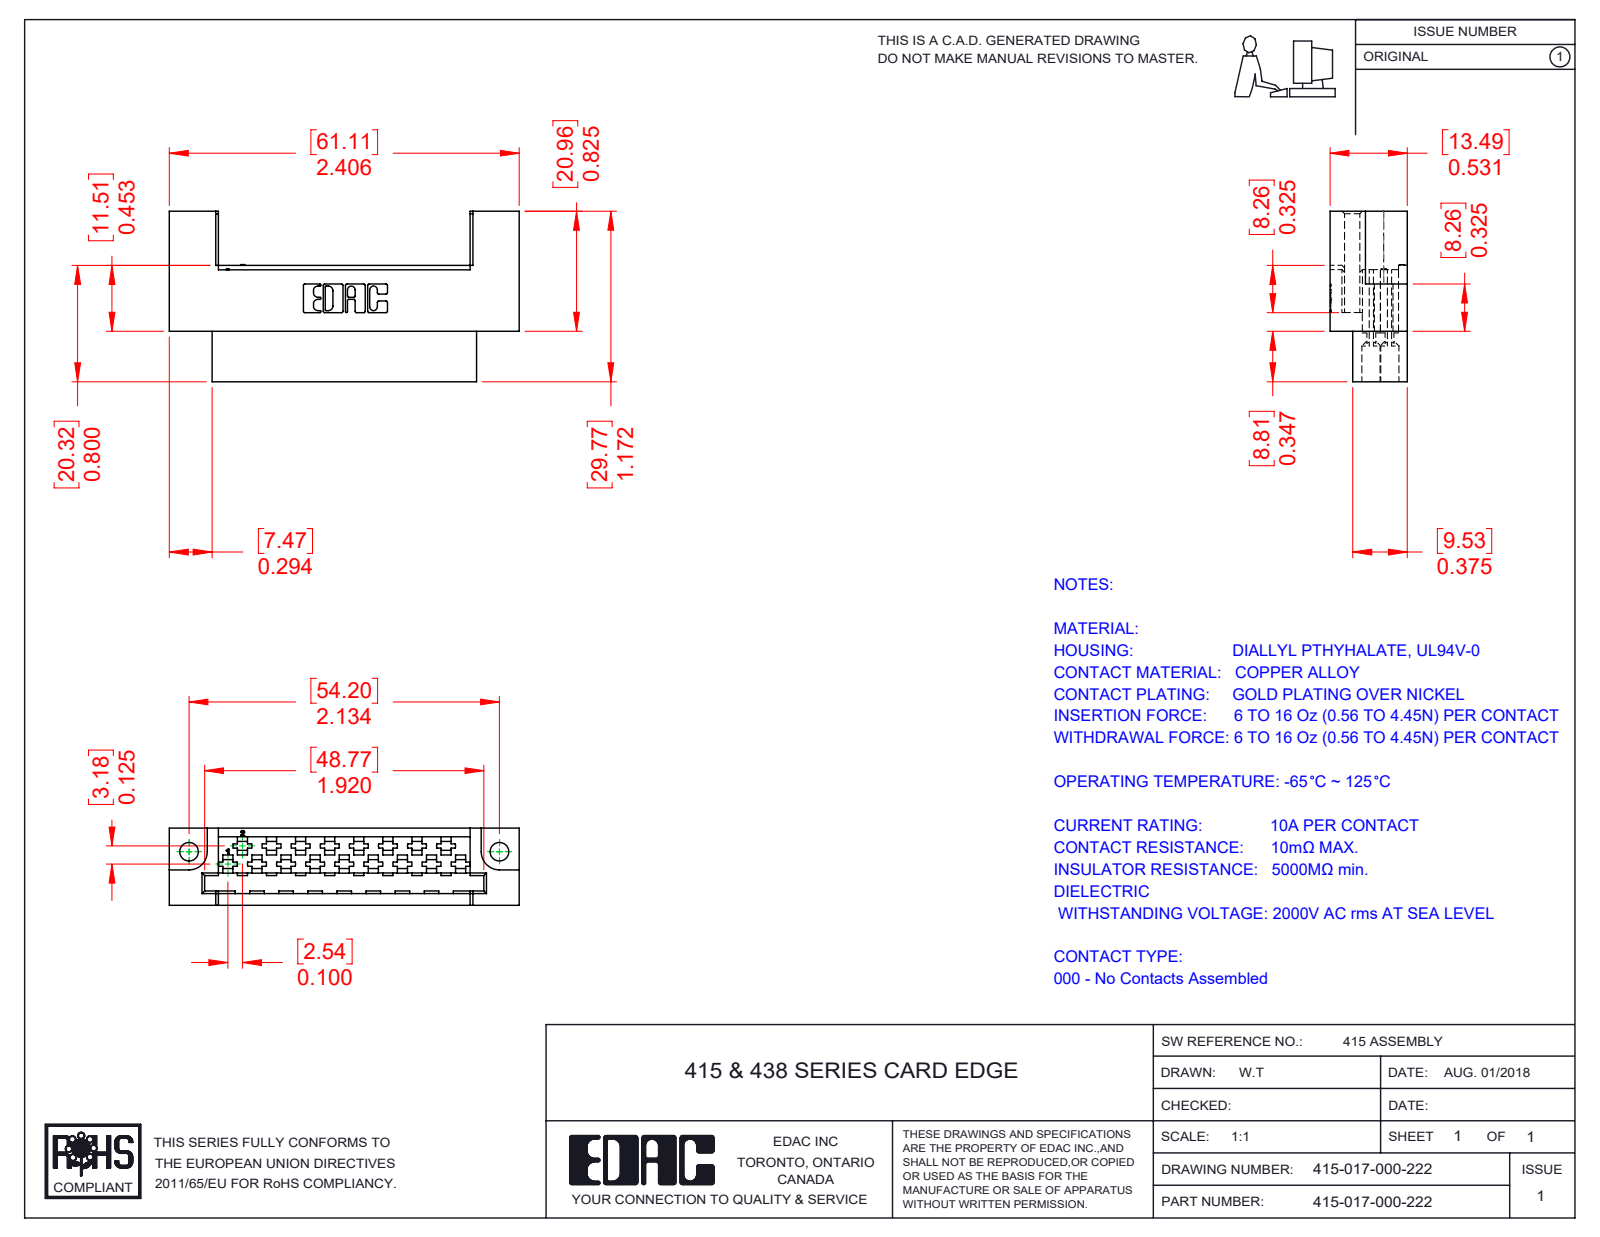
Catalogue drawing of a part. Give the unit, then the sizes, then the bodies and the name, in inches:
Units: inches
Overall size (bounding box): 2.406 × 1.172 × 0.531
Round holes (diameter × count): ⌀0.13 ×17, ⌀0.128 ×2
Partial cylindrical surfaces — rounded edges, fillets, slot ends (radius × count): R0.01 ×22, R0.007 ×6, R0.031 ×6, R0.026 ×3, R0.125 ×2
Main face-to-face distances: 0.531, 0.375, 0.156, 0.048, 0.141, 0.047, 0.029, 0.076, 0.124, 0.078
Hole centre spacings: 0.16, 0.2, 0.325, 0.4, 0.515, 0.6, 0.711, 0.8
Volume: 0.622 in³ · Surface area: 15.06 in²
Bodies: 1 solid, 602 faces (449 planar, 80 cylindrical, 73 other)
Part name (STEP PRODUCT): 415-017-000-222; 415-210-001_415-210-017-222
STEP written by: SolidWorks 2016 (CONFIG_CONTROL_DESIGN)
